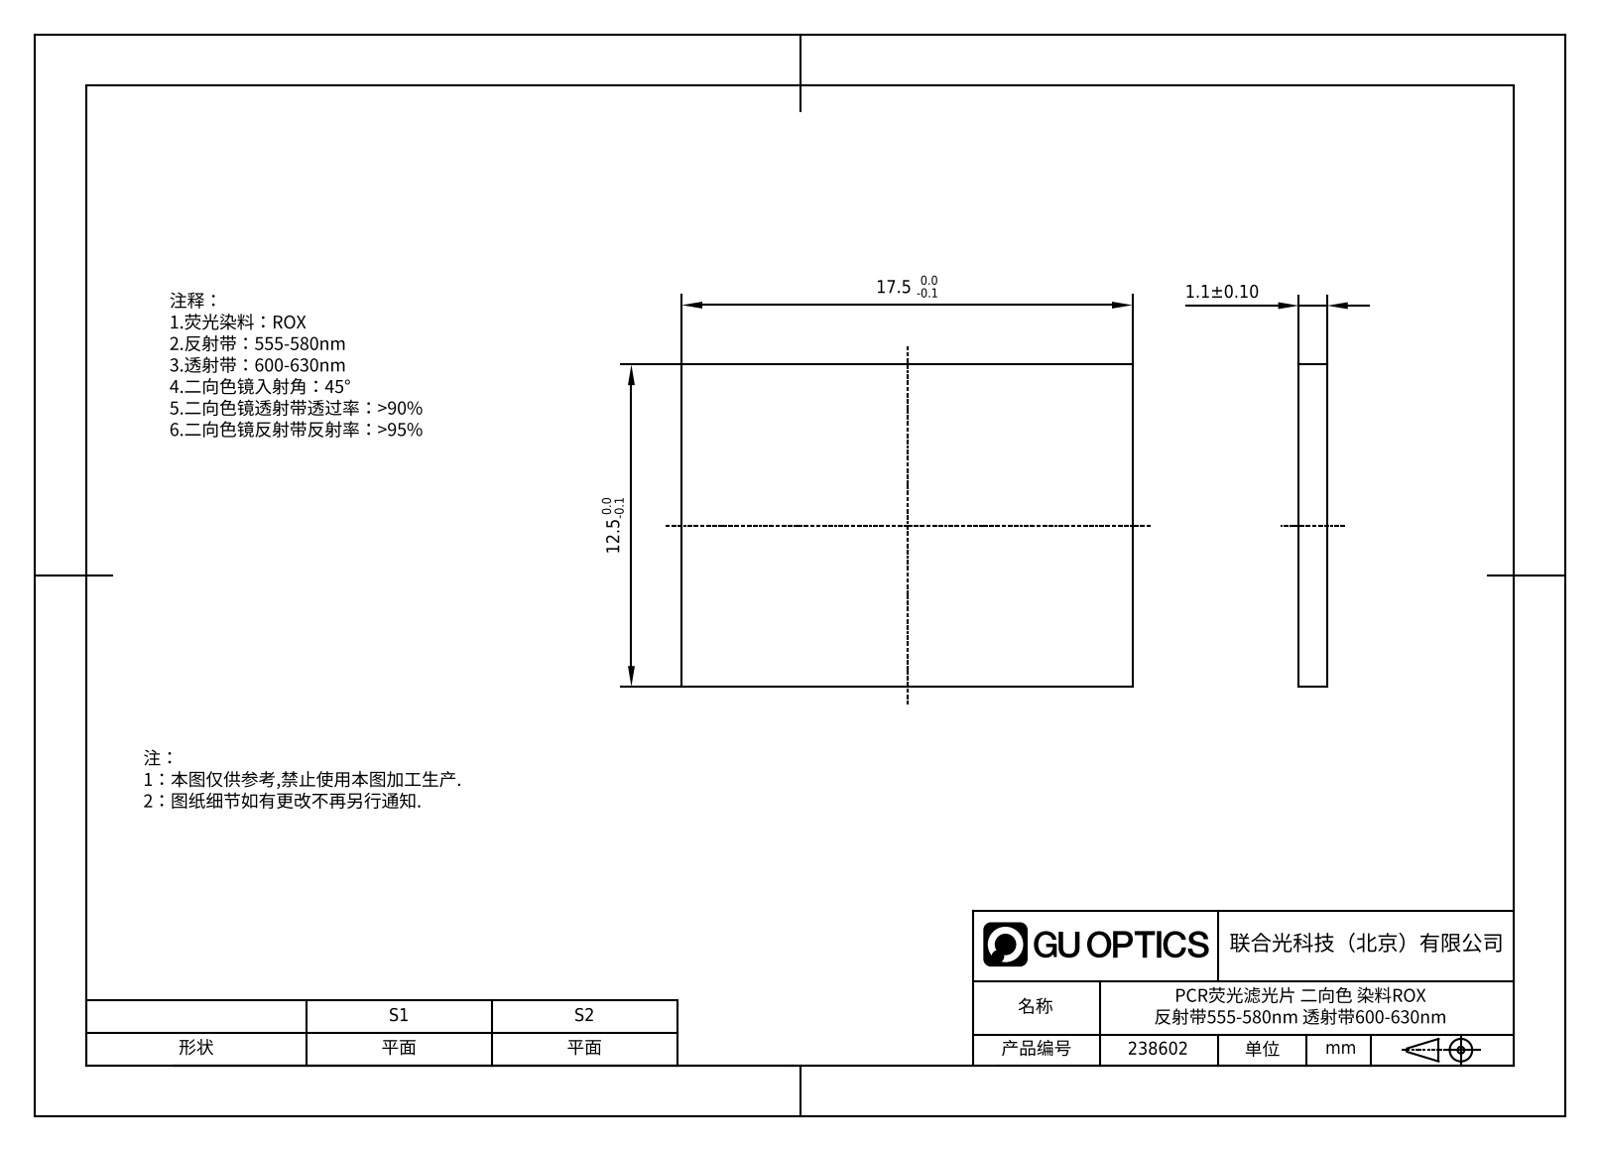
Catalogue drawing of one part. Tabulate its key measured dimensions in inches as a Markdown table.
| quantity | value |
| --- | --- |
| part name | GDMLPH-590-12x17 |
| STEP written by | SolidWorks 2022 (AUTOMOTIVE_DESIGN) |
| units | inches |
| bodies | 1 solid, 6 faces (6 planar, 0 cylindrical, 0 other) |
| overall size | 0.689 × 0.492 × 0.043 |
| volume | 0.015 in³ |
| surface area | 0.781 in² |
| main face-to-face distances | 0.043, 0.492, 0.689 |
